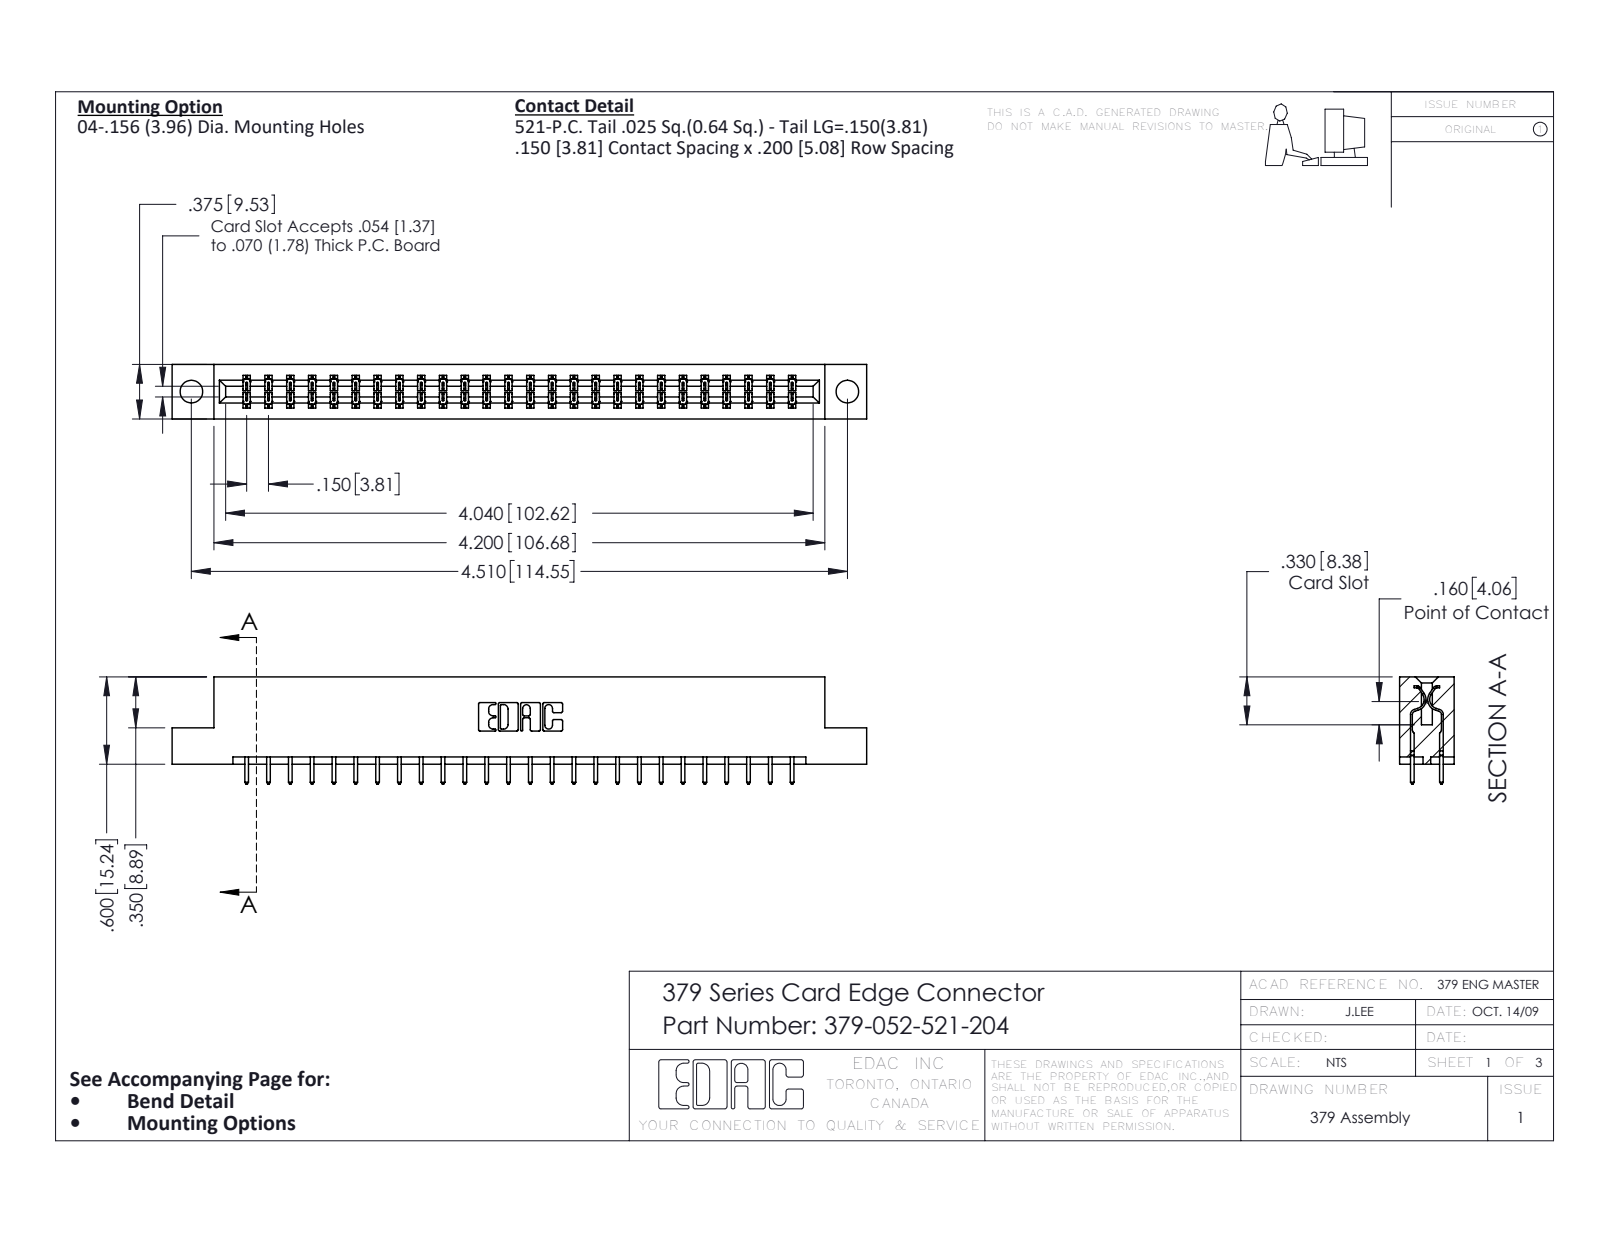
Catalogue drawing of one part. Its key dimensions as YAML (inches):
part_name: "379 Part_Flush - .156 Dia - TH; 379-052-521-204; 345-292-001_345-293-121"
step_written_by: "SolidWorks 2016 (CONFIG_CONTROL_DESIGN)"
units: inches
bodies: {solids: 53, faces: 2818, planar: 1942, cylindrical: 876, other: 0}
overall_size: [4.775, 0.737, 0.375]
volume: 0.77
surface_area: 21.18
round_holes:
  - {diameter: 0.156, count: 2}
partial_cylinders:
  - {radius: 0.006, count: 78}
  - {radius: 0.01, count: 52}
  - {radius: 0.01, count: 22}
  - {radius: 0.007, count: 6}
  - {radius: 0.031, count: 6}
  - {radius: 0.026, count: 3}
  - {radius: 0.014, count: 2}
  - {radius: 0.022, count: 2}
face_to_face_distances: [0.3, 0.075, 0.375, 0.2, 0.1, 0.225, 0.076, 0.15, 0.275, 0.55]
hole_center_spacings: [4.51]
